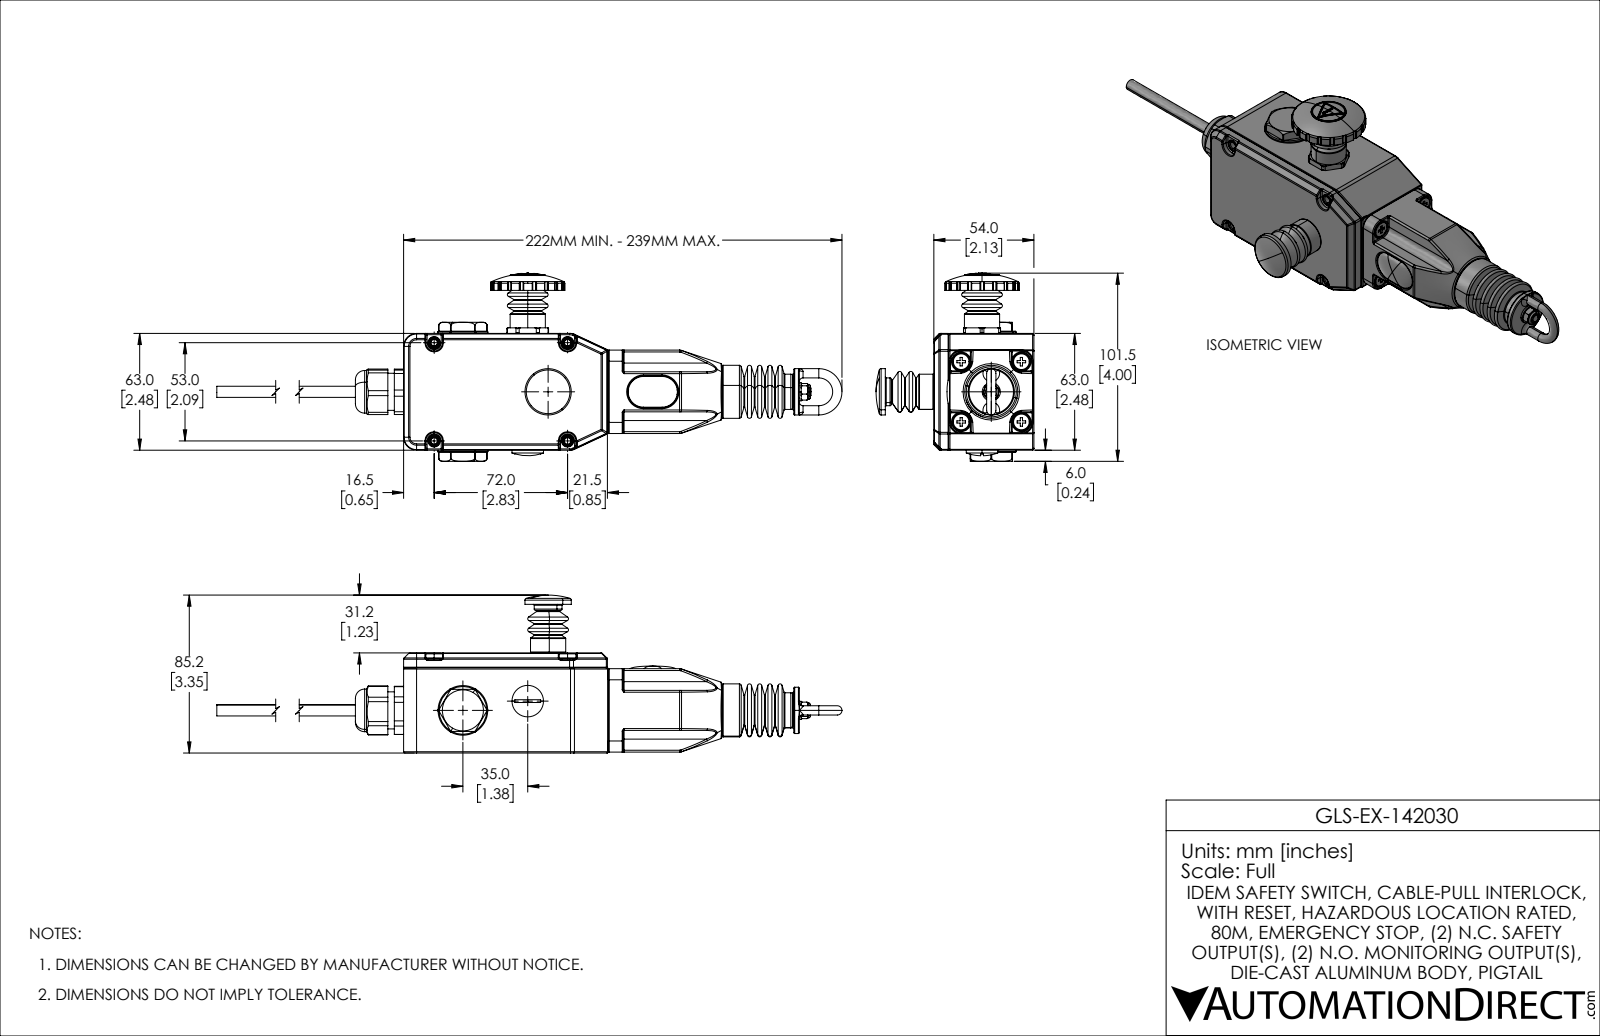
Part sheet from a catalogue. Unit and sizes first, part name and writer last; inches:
Units: inches
Overall size (bounding box): 12.839 × 3.996 × 3.354
Round holes (diameter × count): ⌀0.106 ×6, ⌀0.197 ×6, ⌀0.138 ×5, ⌀0.209 ×5, ⌀0.394 ×5, ⌀0.157 ×4, ⌀0.181 ×4, ⌀0.189 ×4, ⌀0.213 ×4, ⌀0.374 ×4, ⌀0.083 ×3, ⌀0.26 ×3
Round bosses / shafts (diameter × count): ⌀0.244 ×5, ⌀0.236 ×5, ⌀0.335 ×4, ⌀0.197 ×4, ⌀0.173 ×4, ⌀0.748 ×3, ⌀0.984 ×2, ⌀0.63 ×2
Partial cylindrical surfaces — rounded edges, fillets, slot ends (radius × count): R0.02 ×290, R0.008 ×92, R0.039 ×77, R0.031 ×51, R0.028 ×44, R0.012 ×24, R0.006 ×14, R0.004 ×11
Main face-to-face distances: 1.988, 0.118, 2.106, 0.138, 2.48, 1.87, 0.217, 2.126, 0.252, 1.736
Hole centre spacings: 0.905, 1.28, 1.428, 2.378, 3.918, 2.218, 3.626, 0.044
Volume: 13.37 in³ · Surface area: 228.1 in²
Bodies: 25 solids, 3491 faces (822 planar, 1240 cylindrical, 1429 other)
Part name (STEP PRODUCT): GLS-EX-142030
STEP written by: SolidWorks 2021 (AUTOMOTIVE_DESIGN)
